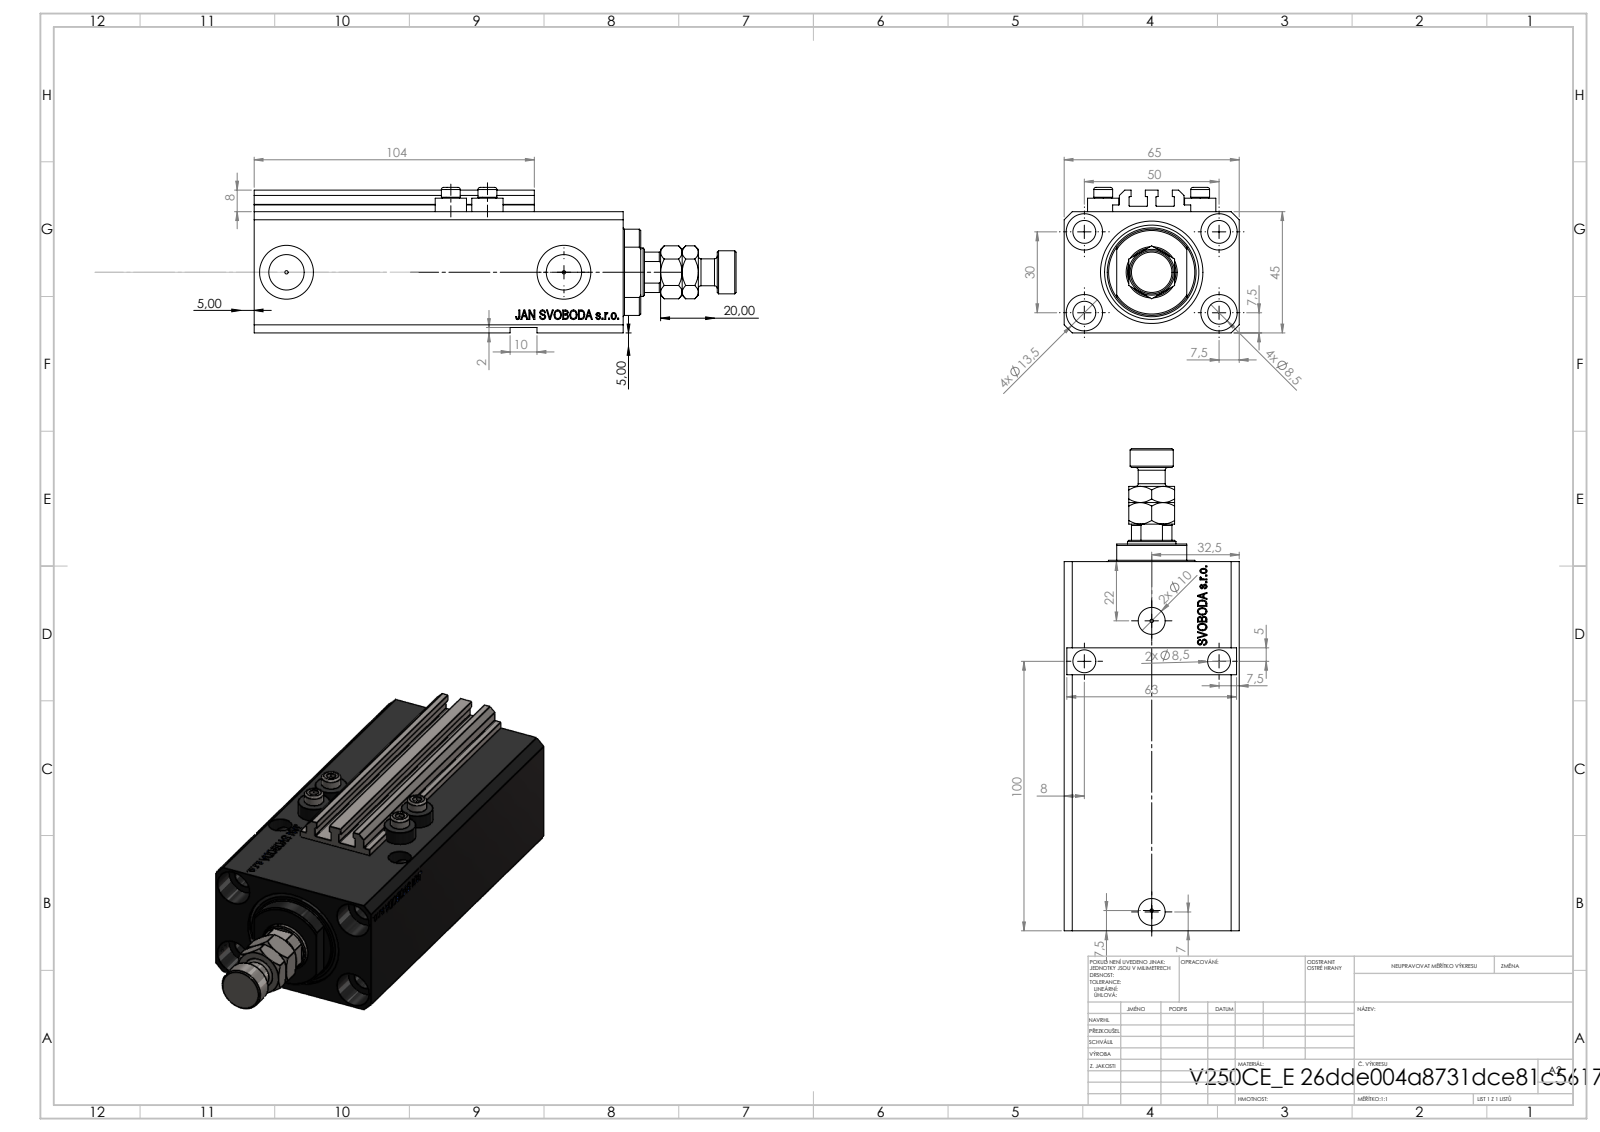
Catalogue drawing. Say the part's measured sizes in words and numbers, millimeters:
The part is named "ALLEN BOLT V250CE; V250CE_E; V250CE_VC_E; MFA (+1 more)". Its 3-D file was written by "SolidWorks 2019 (CONFIG_CONTROL_DESIGN)". It is 9 solids with 1119 faces: 527 planar, 130 cylindrical and 462 other. Overall it measures 178.9 by 65 by 54 millimeters. Its volume is 359 379 cubic millimeters and its surface area 96 696 square millimeters. Round holes: 7 of diameter 8.5, 4 of diameter 1.25, 4 of diameter 4, 4 of diameter 13.5, 2 of diameter 10, 2 of diameter 13.16, 2 of diameter 20, 1 of diameter 18, 1 of diameter 25, 1 of diameter 38. Round bosses or shafts: 4 of diameter 11.6, 4 of diameter 7, 1 of diameter 16, 1 of diameter 10. Partial cylindrical surfaces (rounded edges, fillets, slot ends): 10 of radius 0.2, 1 of radius 8.5, 1 of radius 16. The main face-to-face distances are 45, 65, 47, 2, 111.9, 2.5, 10, 6.9, 6, 137. The hole center spacings are 29.15, 50, 13.6, 15.12, 27.89, 30, 33.62, 36.
